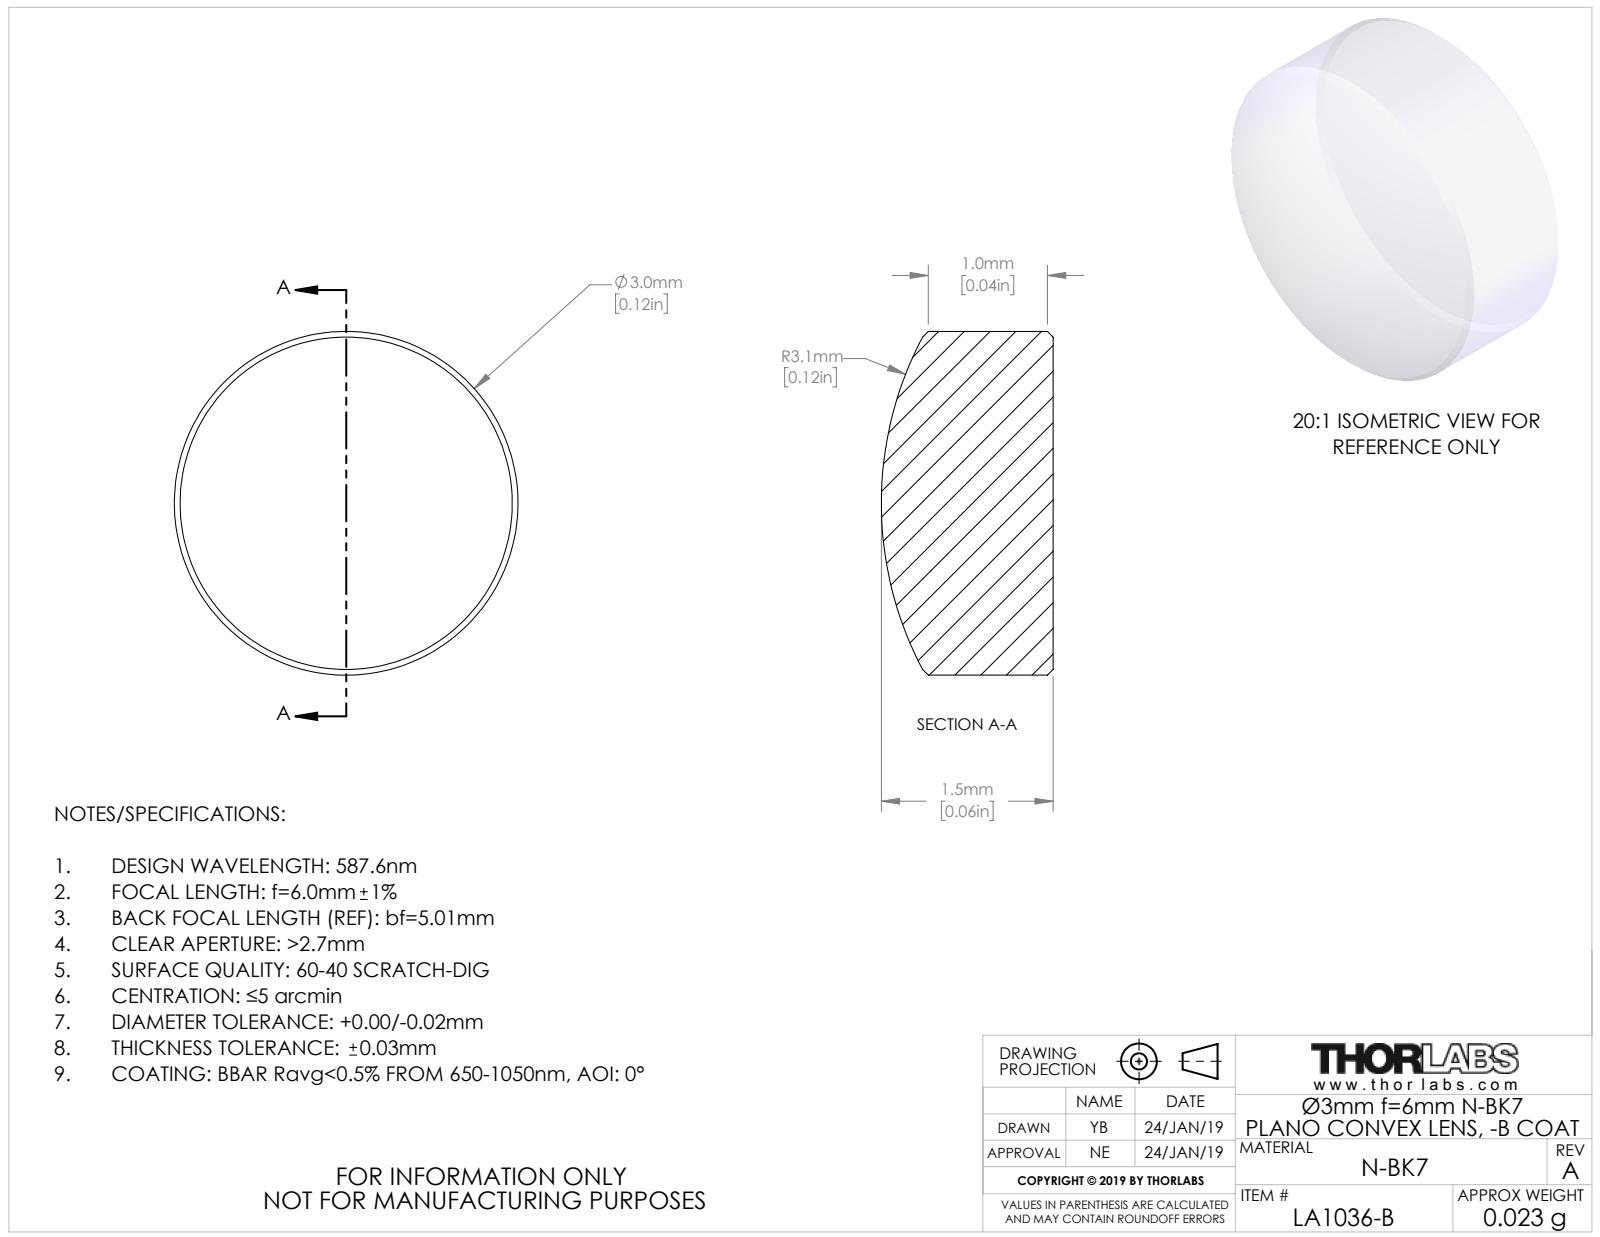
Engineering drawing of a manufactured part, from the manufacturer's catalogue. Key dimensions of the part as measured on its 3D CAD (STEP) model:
Part name (STEP PRODUCT): TTN162604-E0W
STEP written by: SolidWorks 2018 (CONFIG_CONTROL_DESIGN)
Units: millimetres
Bodies: 1 solid, 9 faces (1 planar, 2 cylindrical, 6 other)
Overall size (bounding box): 3 × 3 × 1.5
Volume: 9 mm³ · Surface area: 25 mm²
Round bosses / shafts (diameter × count): ⌀3 ×1
